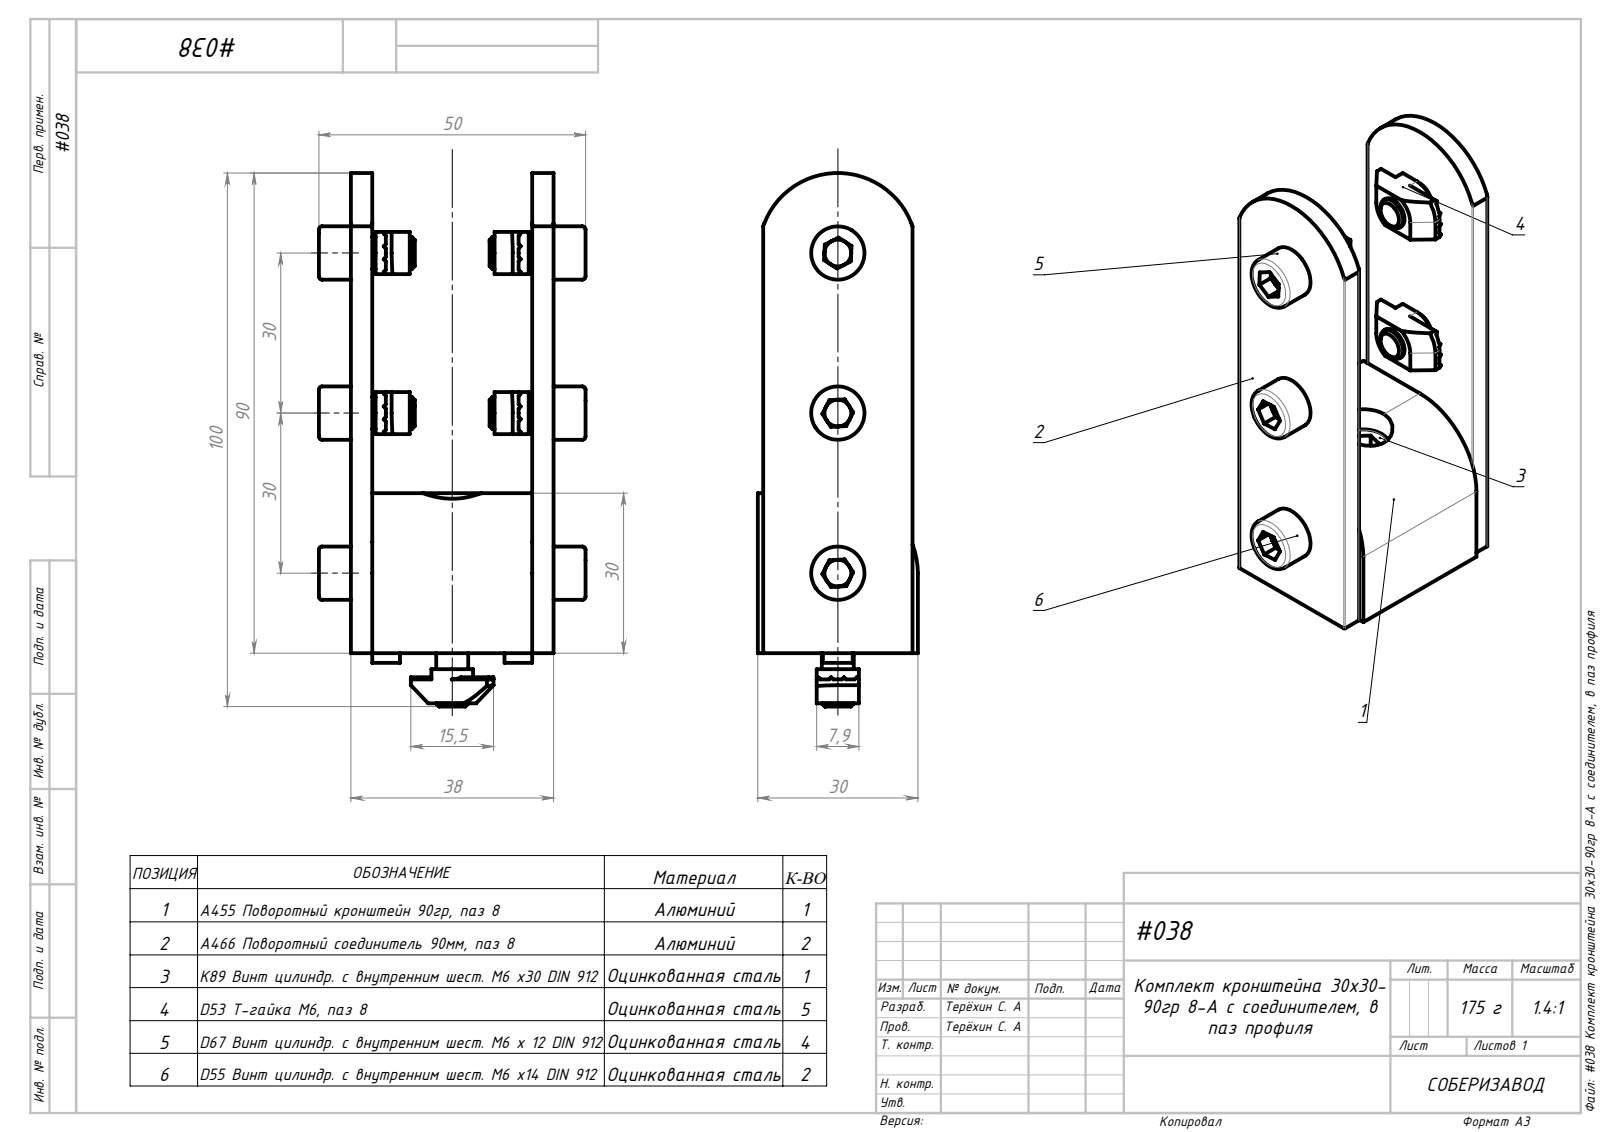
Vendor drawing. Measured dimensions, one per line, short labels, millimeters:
name: #038 Комплект кронштейна 30х30-90гр с соединителем, в паз профиля; D67 Винт цилиндр. с внутренним шест. М6 х 12 DIN 912; D55 Винт цилиндр. с внутренним шест. М6 х14 DIN 912; D53 Т-гайка М6, паз 8_00 (+3 more)
written by: SolidWorks 2021 (AUTOMOTIVE_DESIGN)
unit: mm
bodies: 15 solids, 477 faces (290 planar, 89 cylindrical, 98 other)
size: 100 × 50 × 30
volume: 50 254 mm³; area: 24 966 mm²
holes: 3× ⌀5, 3× ⌀6.4, 1× ⌀5.1, 1× ⌀6.25, 1× ⌀11
bosses: 4× ⌀10, 4× ⌀6
rounds: 10× R4, 8× R0.2, 6× R6.87, 1× R14.8, 1× R15
face distances: 4, 34, 30, 38, 29, 1, 28, 10, 11.05, 7.9
hole spacings: 30, 60
